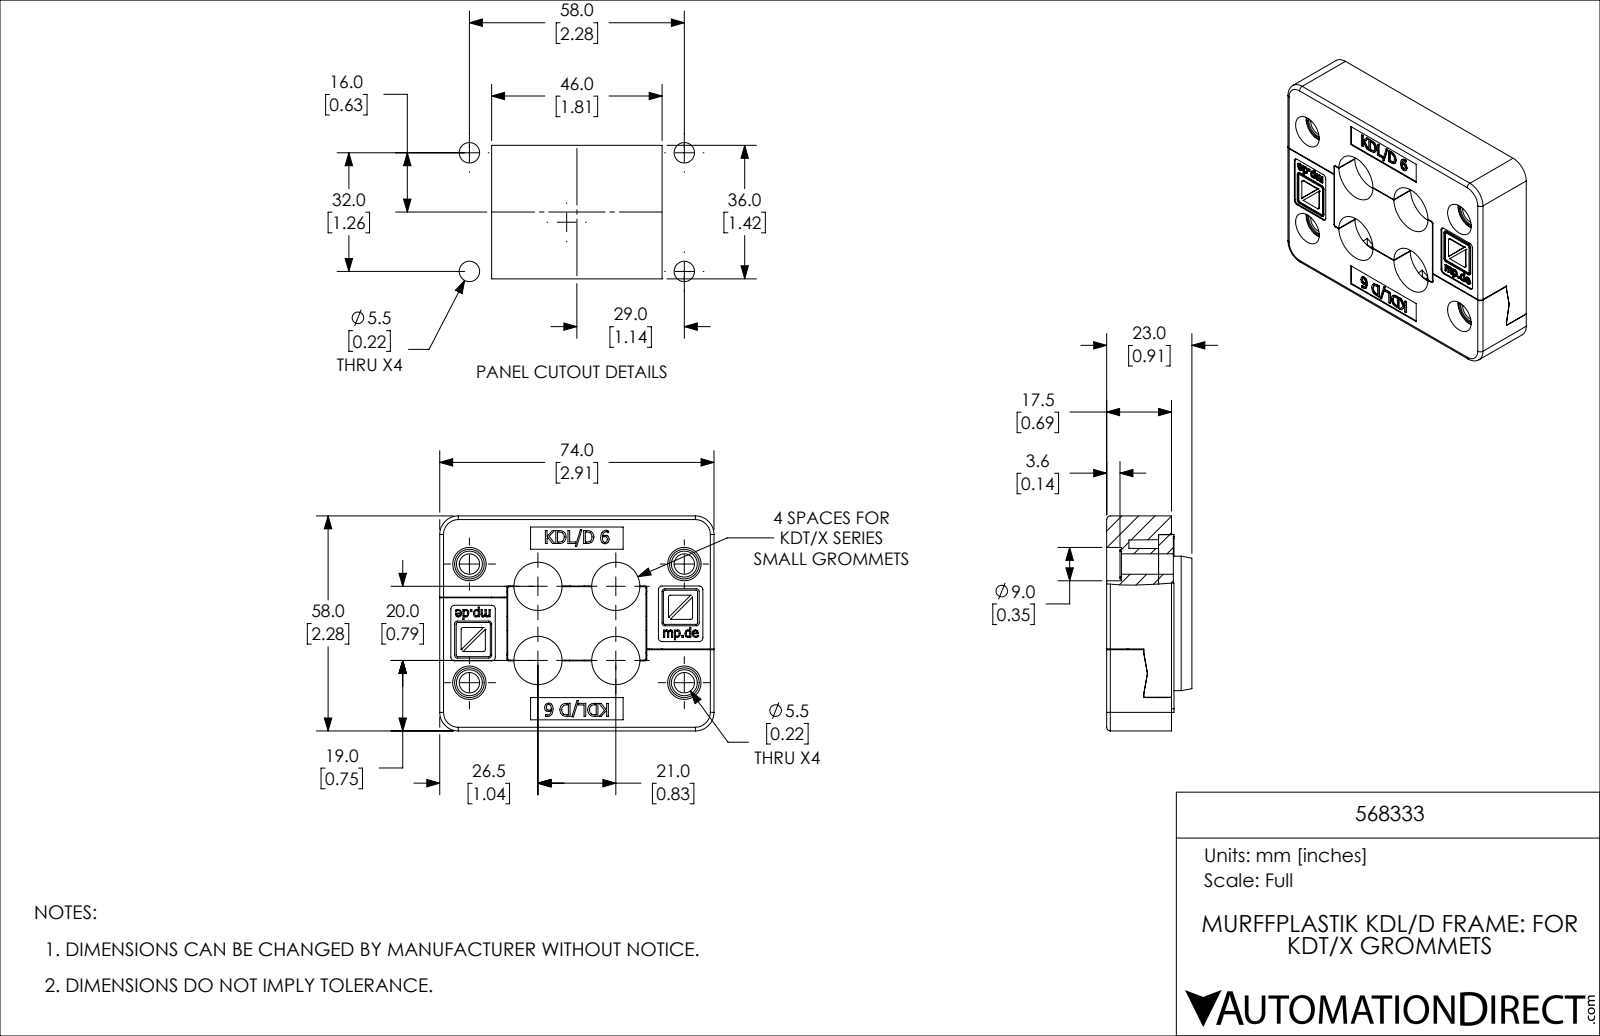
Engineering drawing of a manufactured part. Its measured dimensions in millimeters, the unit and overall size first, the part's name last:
Units: millimetres
Overall size (bounding box): 74 × 58 × 23
Round holes (diameter × count): ⌀5 ×6, ⌀5.5 ×4, ⌀7 ×4, ⌀9 ×4, ⌀13 ×4, ⌀15 ×4, ⌀6 ×2
Round bosses / shafts (diameter × count): ⌀8 ×4
Partial cylindrical surfaces — rounded edges, fillets, slot ends (radius × count): R0.5 ×42, R1 ×30, R0.4 ×12, R0.8 ×8, R0.2 ×4, R0.3 ×4, R2 ×4, R5 ×4
Main face-to-face distances: 14, 5, 4, 3.5, 0.5, 53, 8, 18, 6, 9
Hole centre spacings: 19.5, 21, 31.3, 31.9, 40, 47.3, 7.7, 9.9
Volume: 58 580 mm³ · Surface area: 34 450 mm²
Bodies: 4 solids, 1163 faces (669 planar, 235 cylindrical, 259 other)
Part name (STEP PRODUCT): 568333
STEP written by: SolidWorks 2019 (CONFIG_CONTROL_DESIGN)
